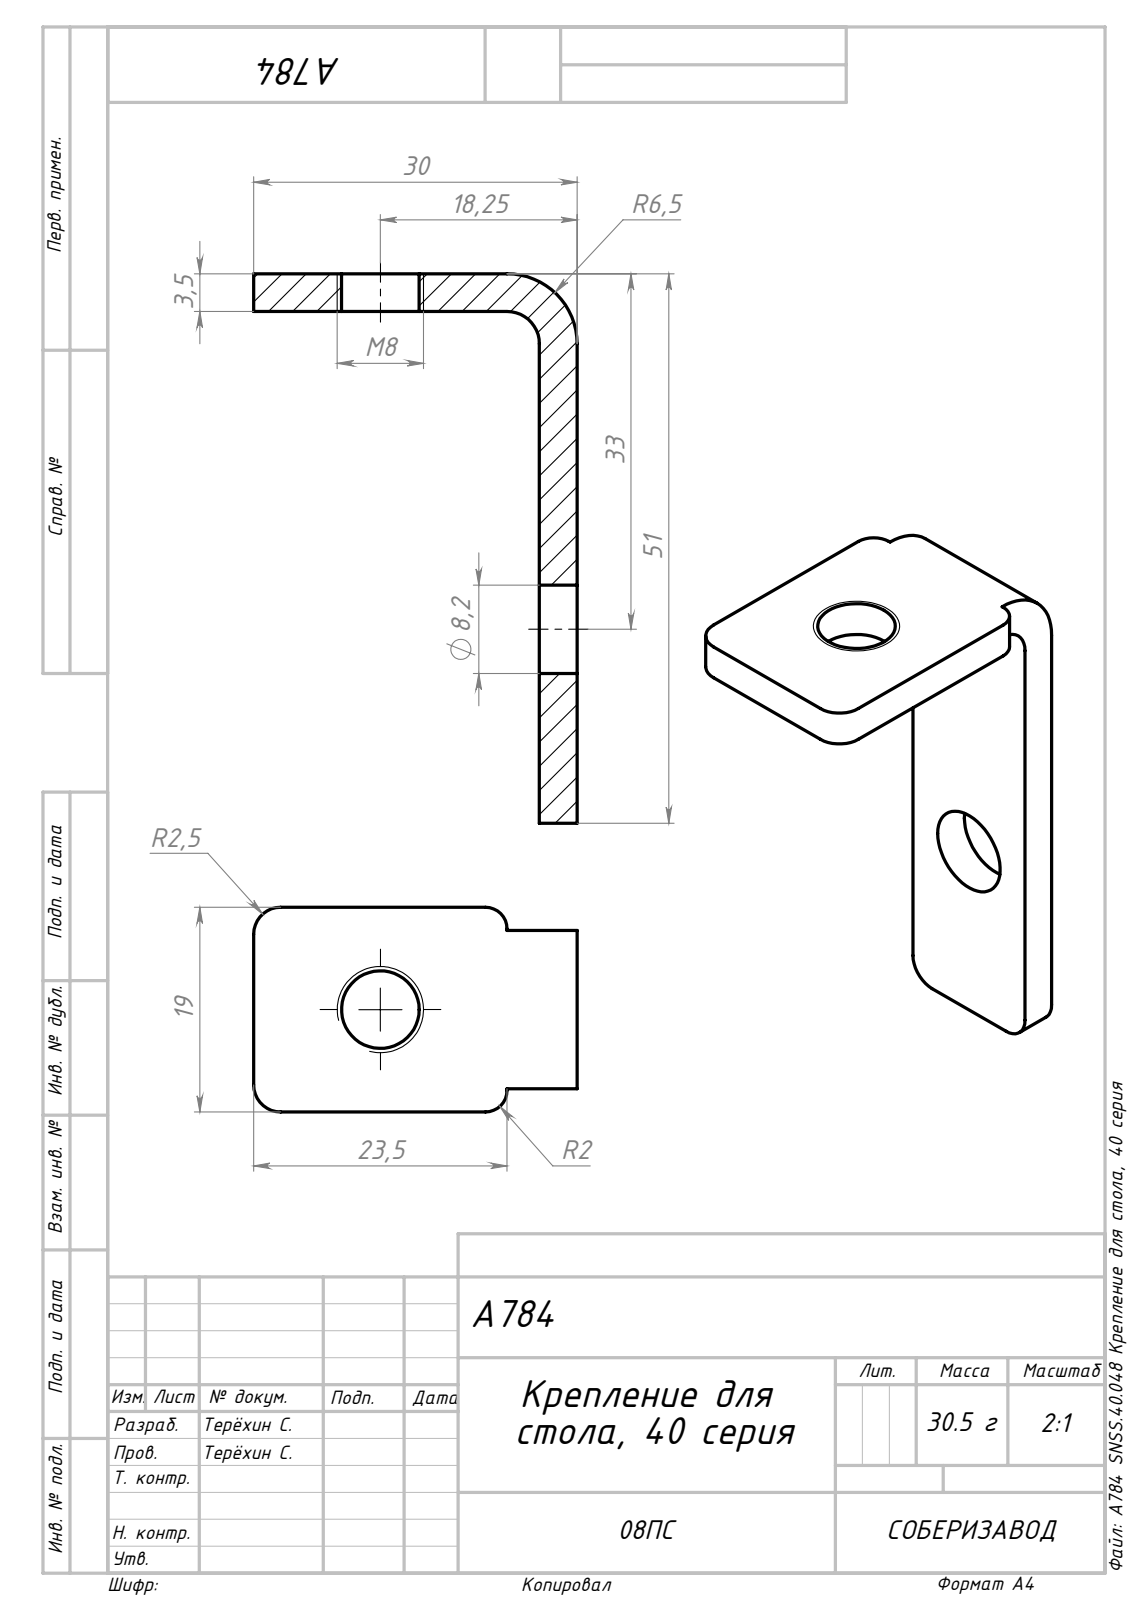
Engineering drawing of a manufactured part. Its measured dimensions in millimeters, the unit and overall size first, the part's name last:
Units: millimetres
Overall size (bounding box): 51 × 30 × 19
Round holes (diameter × count): ⌀7.2 ×1, ⌀8.2 ×1
Partial cylindrical surfaces — rounded edges, fillets, slot ends (radius × count): R2.5 ×4, R2 ×2, R3 ×1, R6.5 ×1
Main face-to-face distances: 3.5, 14.7, 2.15, 16.85, 19, 26.5, 30, 47.5, 51, 23.5
Volume: 3 884 mm³ · Surface area: 3 029 mm²
Bodies: 1 solid, 26 faces (14 planar, 12 cylindrical, 0 other)
Part name (STEP PRODUCT): Сборка3; A784 SNSS.40.048 Крепление для стола, 40 серия_00
STEP written by: SolidWorks 2022 (AUTOMOTIVE_DESIGN)
